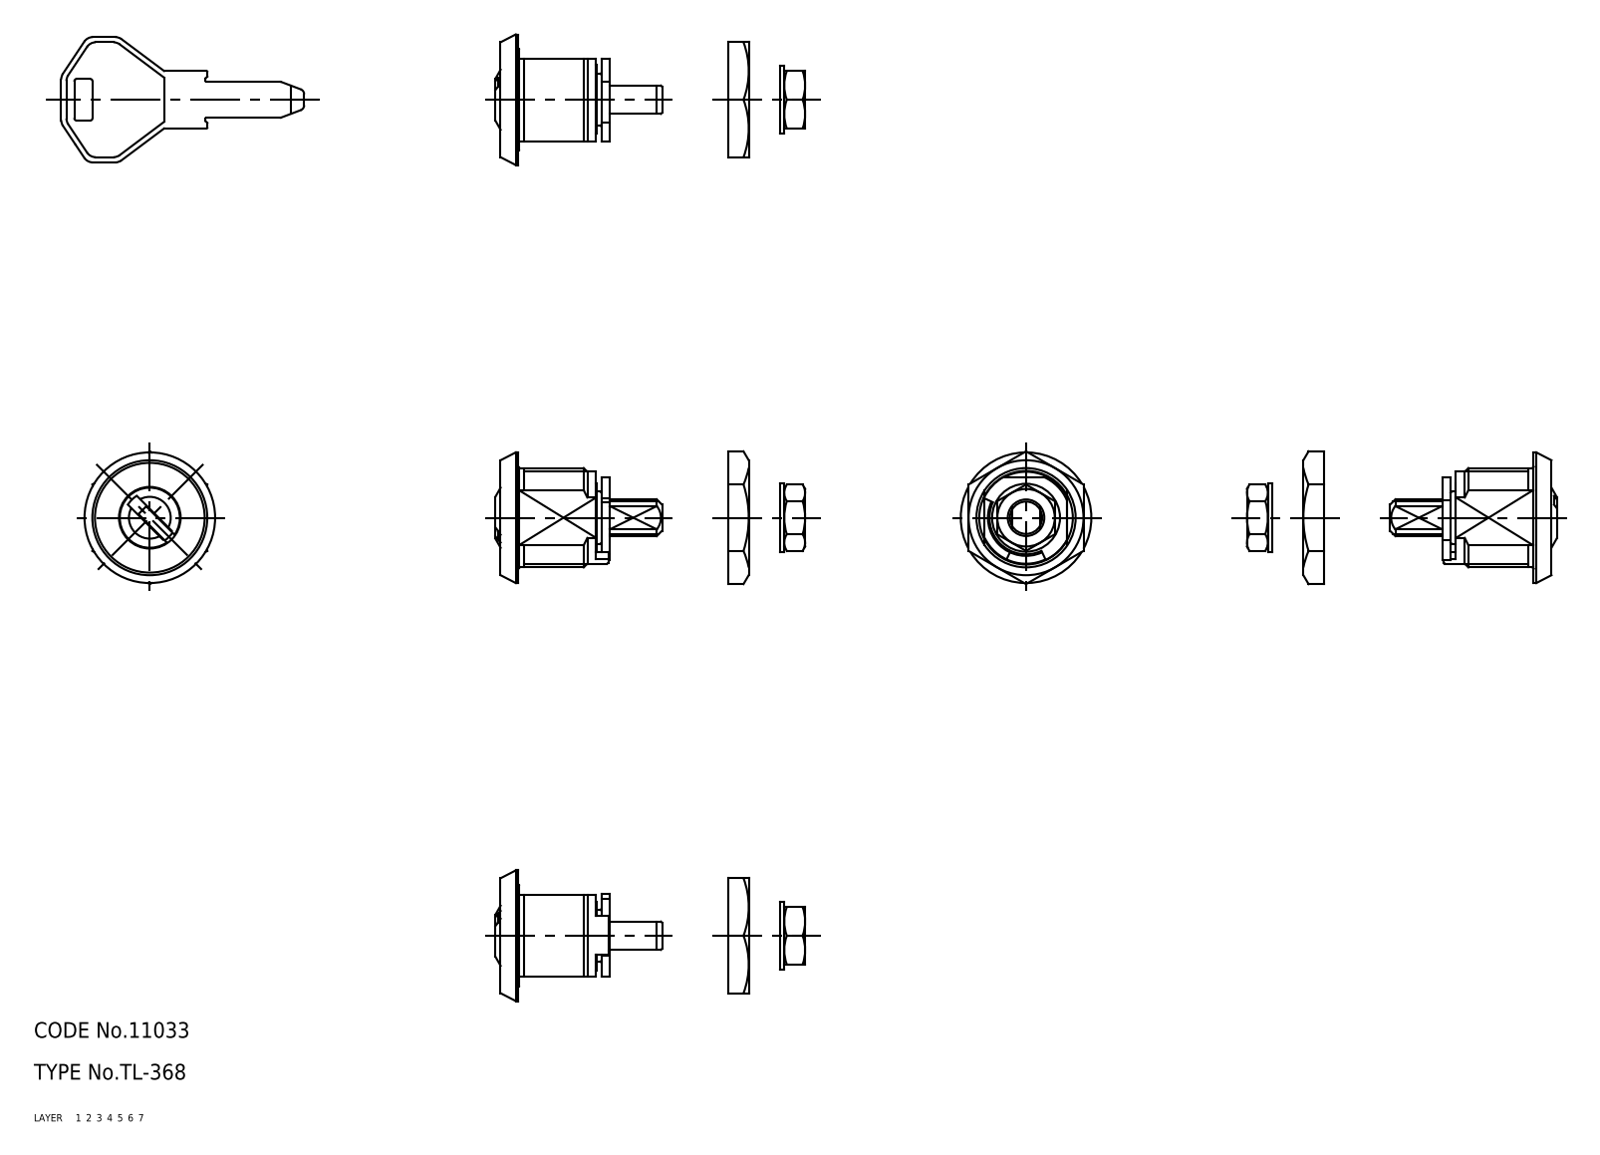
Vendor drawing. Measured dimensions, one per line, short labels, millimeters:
name: 67118224; 67118237; 67118250; 67118263 (+2 more)
written by: CADfix (AUTOMOTIVE_DESIGN)
unit: mm
bodies: 6 solids, 214 faces (0 planar, 0 cylindrical, 214 other)
size: 115.02 × 25.4 × 25
volume: 7 898 mm³; area: 5 768 mm²
